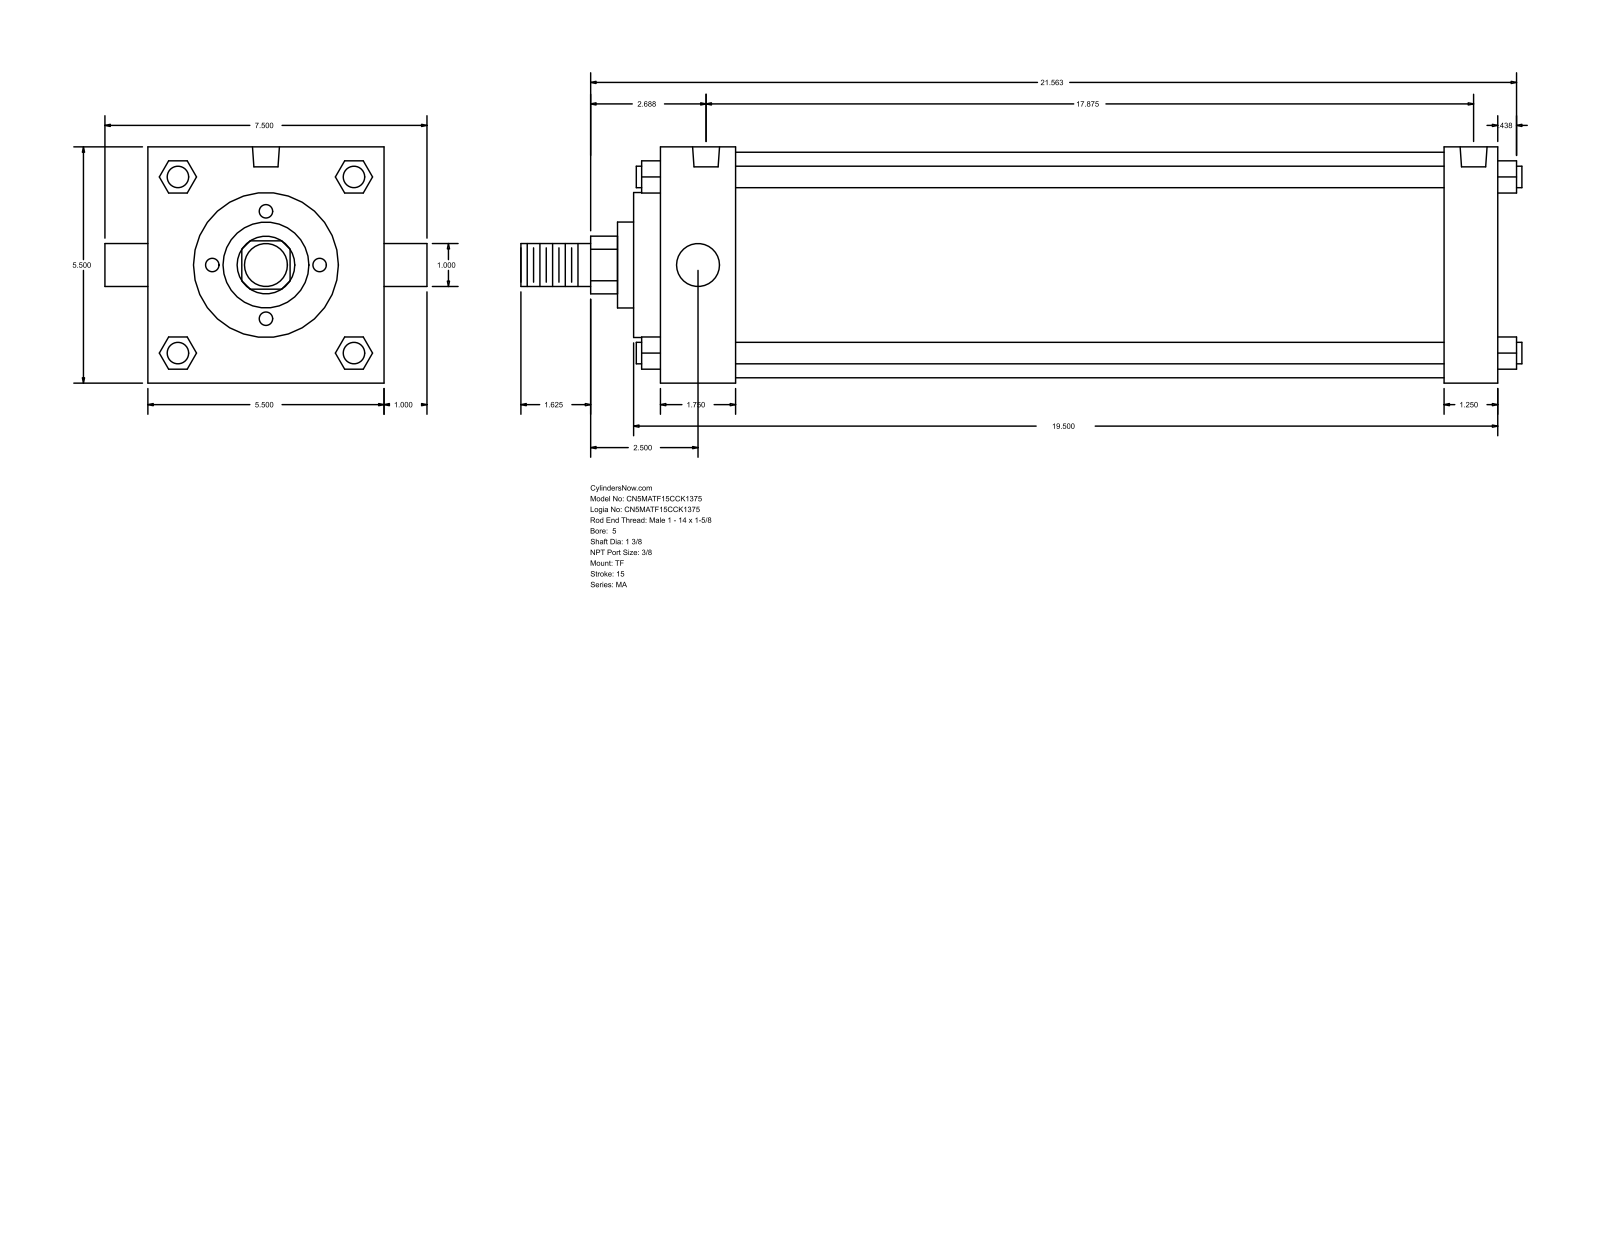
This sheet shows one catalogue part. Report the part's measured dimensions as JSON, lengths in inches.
{"part_name": "MA_TF__0500_1.375", "step_written_by": "GSSL Pune (CONFIG_CONTROL_DESIGN)", "units": "inches", "bodies": {"solids": 0, "faces": 122, "planar": 93, "cylindrical": 29, "other": 0}, "overall_size": [23.313, 7.5, 5.5], "round_holes": [[0.437, 3], [0.627, 2]], "round_bosses_or_shafts": [[0.5, 4], [1, 2], [5.25, 1], [3.375, 1], [2, 1], [1.375, 1]], "partial_cylinders_radius": [[0.672, 1]], "face_to_face_distances": [5.5, 19.5, 18.25, 1.25, 1.75, 16.5, 17.75, 0.625, 2.375, 18.875], "hole_center_spacings": [0.188, 17.687, 17.5, 17.875]}
